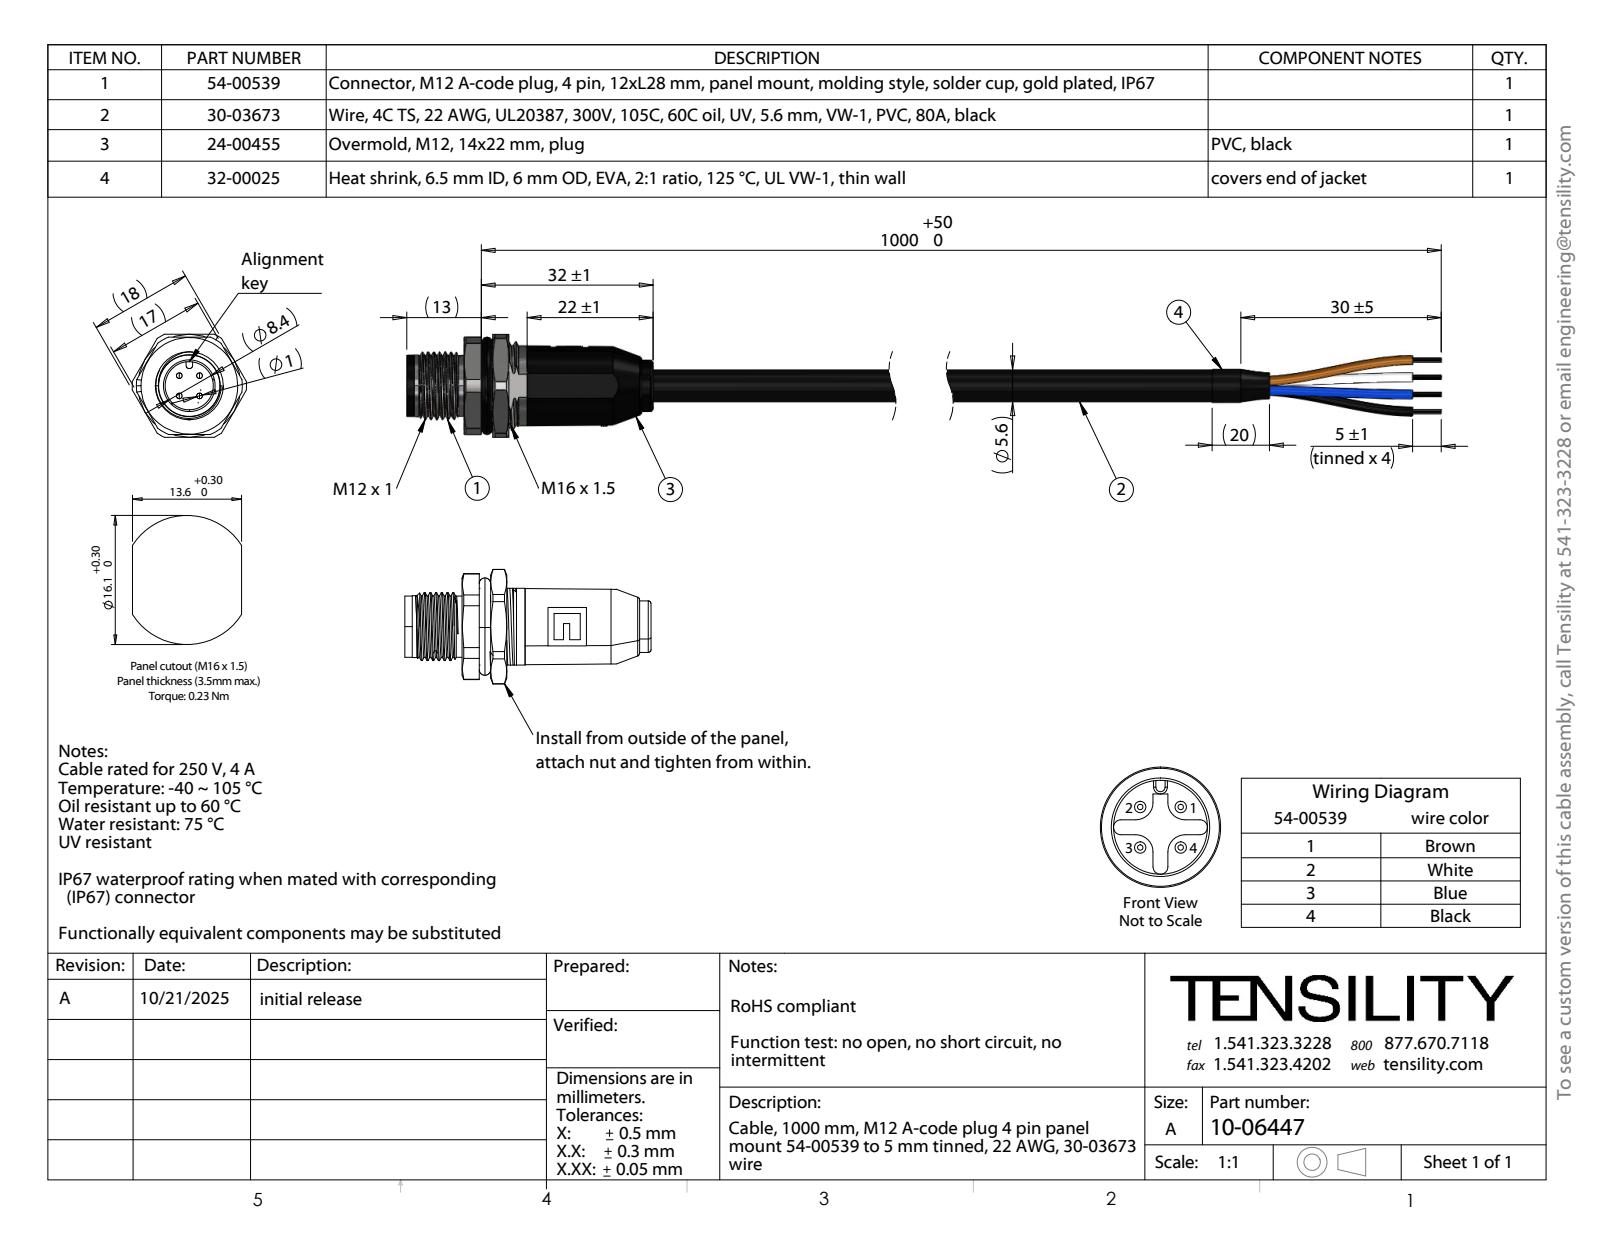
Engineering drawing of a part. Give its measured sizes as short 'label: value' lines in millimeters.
name: 54-00539; 32-00025_10 mm; 30-03673_spec; 24-00455 (+2 more)
written by: SolidWorks 2025 (CONFIG_CONTROL_DESIGN)
unit: mm
bodies: 150 solids, 1215 faces (474 planar, 576 cylindrical, 165 other)
size: 227.99 × 20 × 18
volume: 9 543 mm³; area: 34 133 mm²
holes: 4× ⌀1.6, 3× ⌀1, 1× ⌀0.96, 1× ⌀3.88, 1× ⌀4.28, 1× ⌀6.5, 1× ⌀8.4, 1× ⌀9.4, 1× ⌀9.6, 1× ⌀12.2, 1× ⌀14.7
bosses: 4× ⌀1.5, 4× ⌀1.4, 1× ⌀13.94, 1× ⌀12.5, 1× ⌀11.86, 1× ⌀11, 1× ⌀10.8, 1× ⌀10.7
rounds: 2× R0.5, 1× R7.04, 1× R7.9, 1× R9.25, 1× R10
face distances: 8, 11, 2, 0.5, 1.5, 3, 17.5, 18, 10, 2.8
hole spacings: 0.48, 0.37, 1.62, 0.31, 0.33, 1.78, 0.32, 1.45
